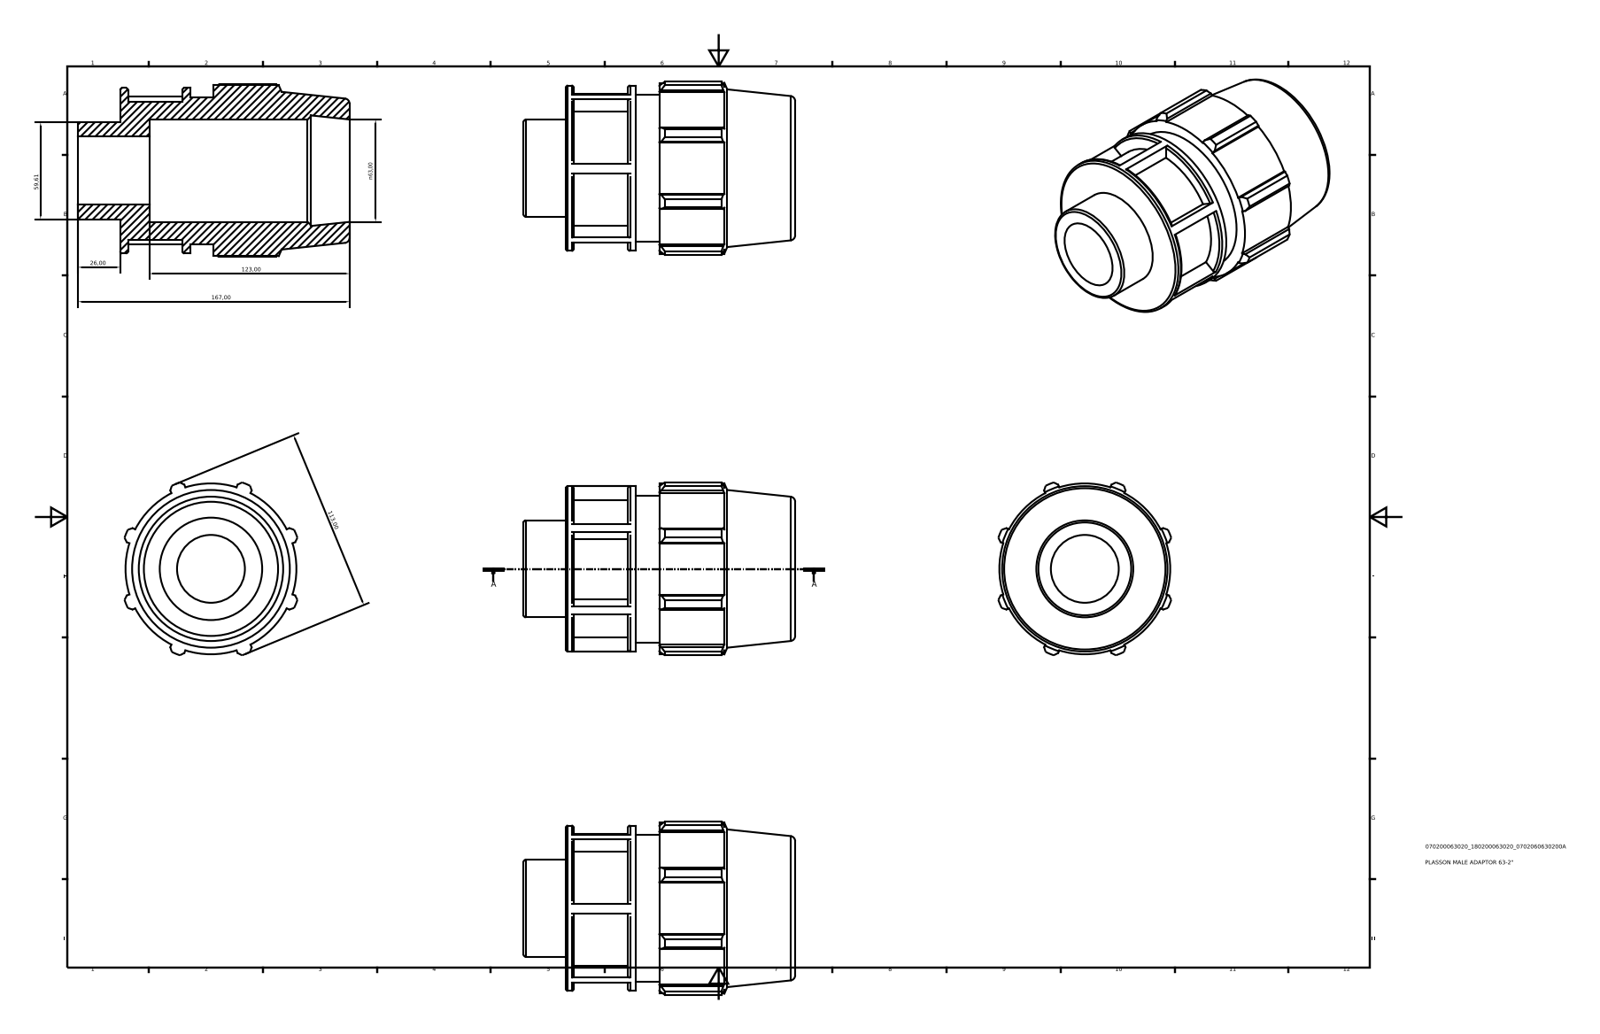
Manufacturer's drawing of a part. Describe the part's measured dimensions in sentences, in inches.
The part is named "070200063020_180200063020". Its 3-D file was written by "Autodesk Inventor 2015 (AUTOMOTIVE_DESIGN)". It is 1 solid with 117 faces: 63 planar, 27 cylindrical and 27 other. Overall it measures 6.575 by 4.186 by 4.186 inches. Its volume is 39.23 cubic inches and its surface area 159.4 square inches. Round holes: 1 of diameter 1.643, 1 of diameter 2.48. Round bosses or shafts: 1 of diameter 4.004, 1 of diameter 3.559, 1 of diameter 3.337, 1 of diameter 2.347. Partial cylindrical surfaces (rounded edges, fillets, slot ends): 1 of radius 2.069, 1 of radius 2.224. The main face-to-face distances are 0.188, 1.503, 3.287, 2.264, 5.551, 0.761, 4.048, 1.315, 2.076, 5.363.
